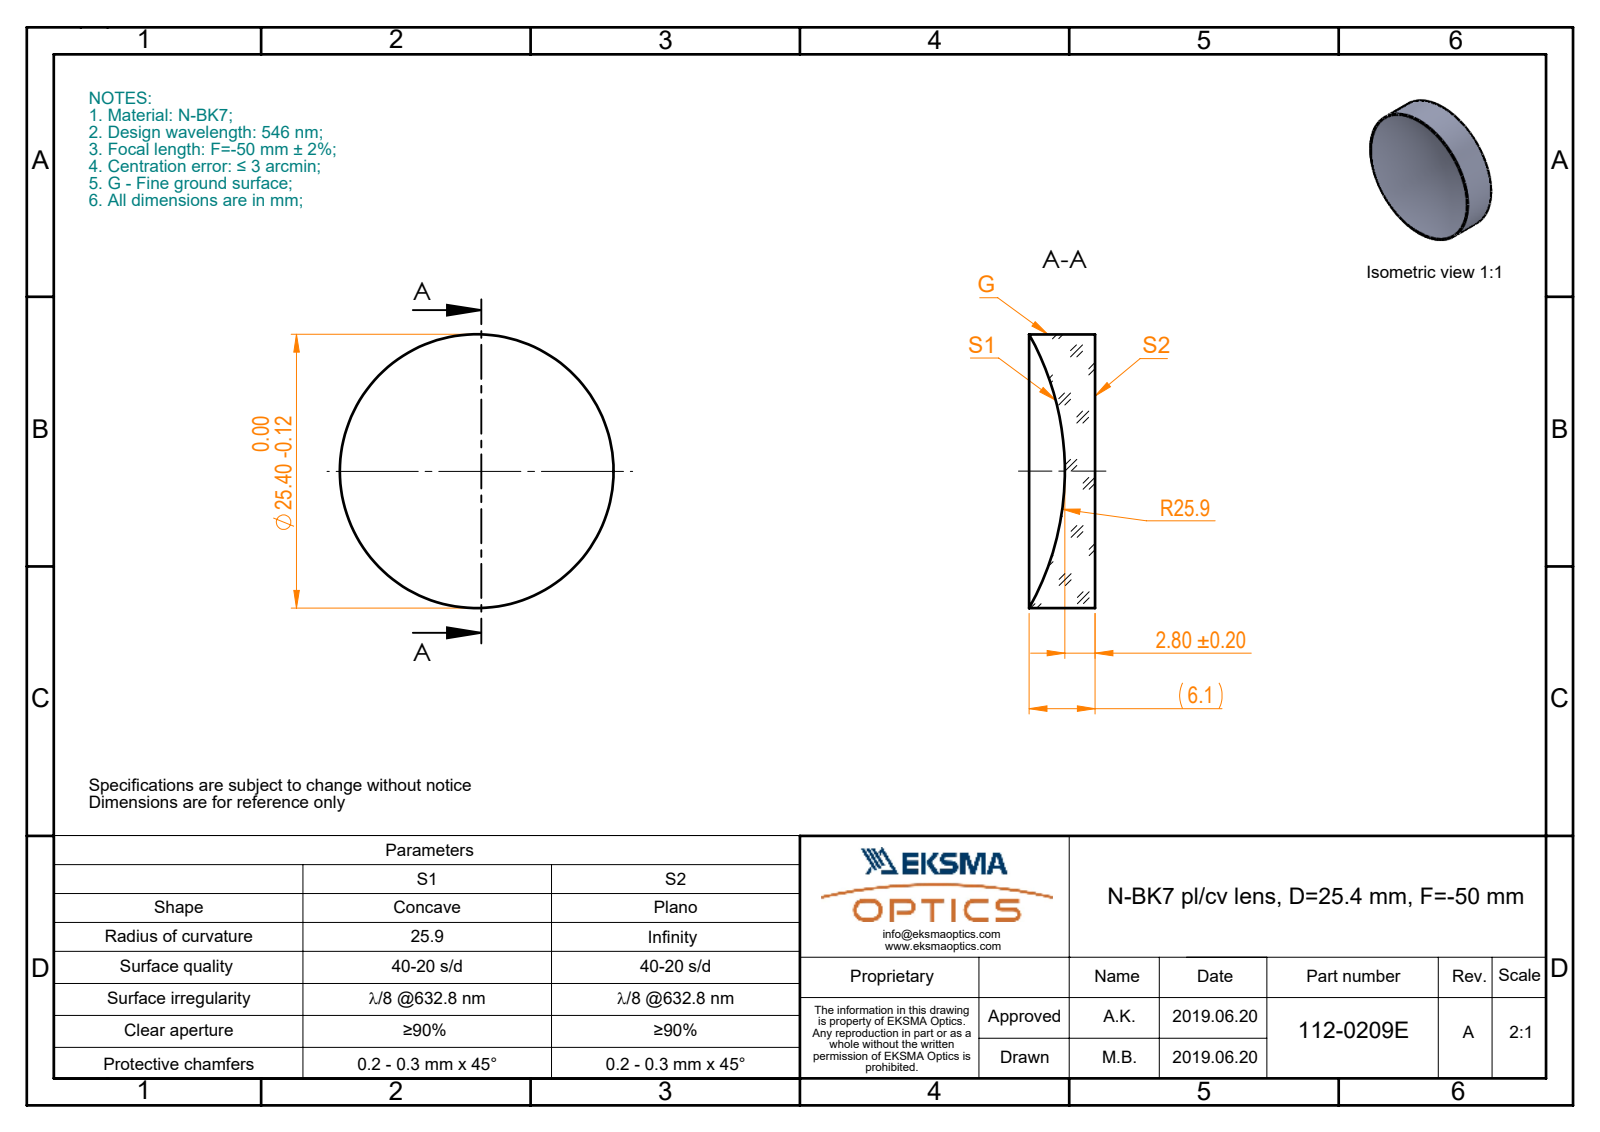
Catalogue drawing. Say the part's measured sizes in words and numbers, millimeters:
The part is named "112-0209E BK7 pl-cv 25.4 F-50". Its 3-D file was written by "SolidWorks 2017 (CONFIG_CONTROL_DESIGN)". It is 1 solid with 5 faces: 1 planar, 2 cylindrical and 2 other. Overall it measures 25.4 by 25.4 by 6.12 millimeters. Its volume is 2 241 cubic millimeters and its surface area 1 537 square millimeters. Round bosses or shafts: 1 of diameter 25.4.
